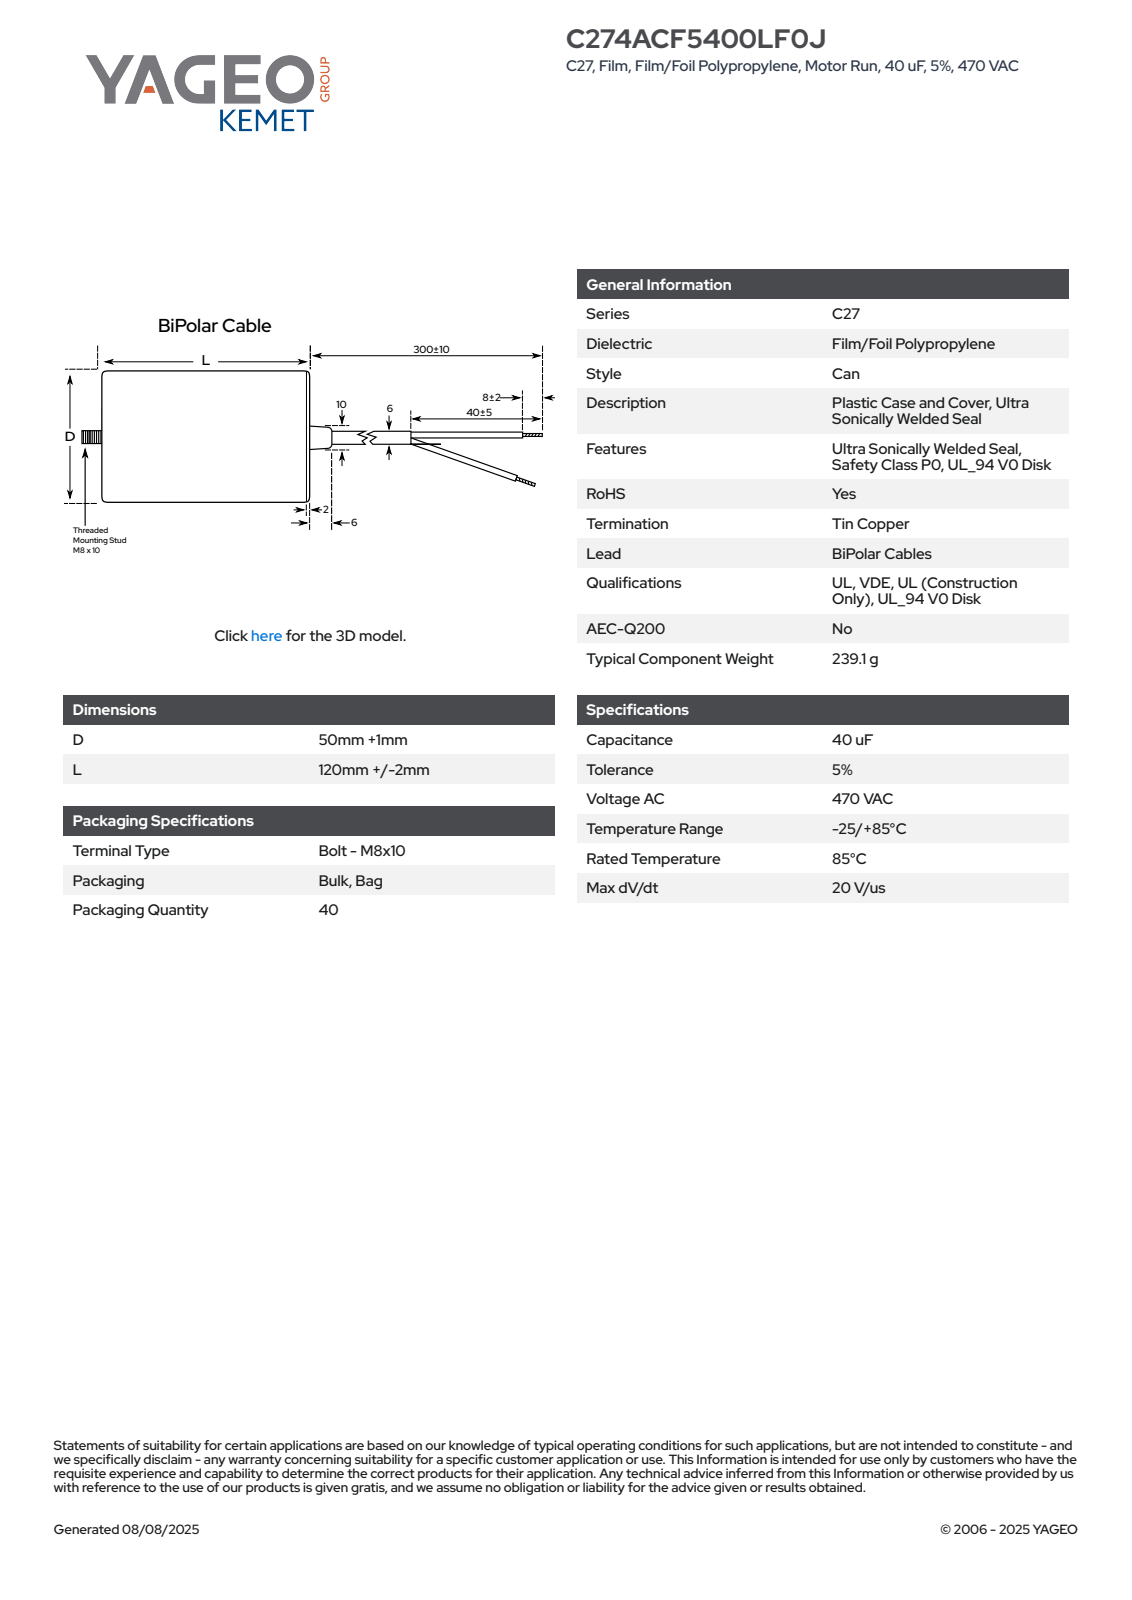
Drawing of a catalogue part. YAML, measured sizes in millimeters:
part_name: "CFM_KC27BI_50X120_D51L122"
step_written_by: "SolidWorks 2014 (AUTOMOTIVE_DESIGN)"
units: millimeters
bodies: {solids: 2, faces: 82, planar: 28, cylindrical: 15, other: 39}
overall_size: [138, 51.01, 51]
volume: 246570
surface_area: 24336
round_holes:
  - {diameter: 47, count: 1}
round_bosses_or_shafts:
  - {diameter: 51, count: 1}
  - {diameter: 8, count: 1}
partial_cylinders:
  - {radius: 25.51, count: 1}
face_to_face_distances: [120, 122, 2, 10, 130, 132, 138, 128, 8, 6]
